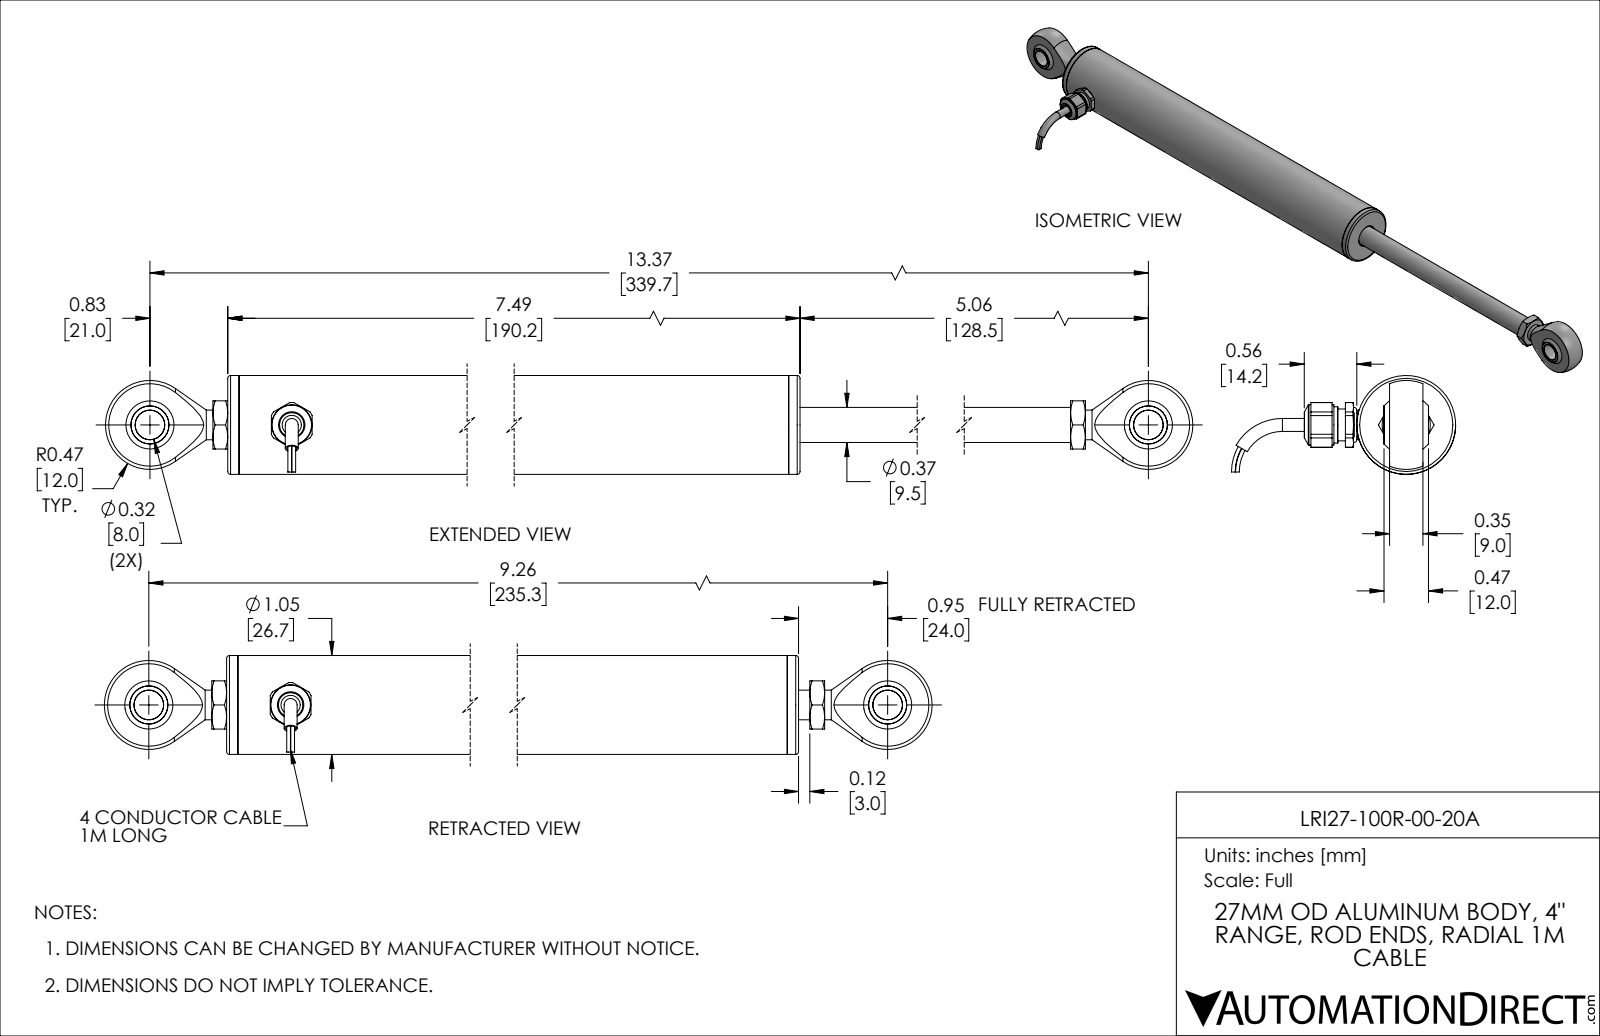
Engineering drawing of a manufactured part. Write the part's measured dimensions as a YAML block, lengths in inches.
part_name: "LRI27-100R-00-20A"
step_written_by: "SolidWorks 2019 (AUTOMOTIVE_DESIGN)"
units: inches
bodies: {solids: 25, faces: 279, planar: 108, cylindrical: 83, other: 88}
overall_size: [10.088, 2.382, 1.05]
volume: 4.474
surface_area: 92.13
round_holes:
  - {diameter: 0.268, count: 2}
  - {diameter: 0.106, count: 1}
  - {diameter: 0.138, count: 1}
  - {diameter: 0.156, count: 1}
  - {diameter: 0.187, count: 1}
  - {diameter: 0.201, count: 1}
  - {diameter: 0.205, count: 1}
  - {diameter: 0.25, count: 1}
  - {diameter: 0.274, count: 1}
  - {diameter: 0.313, count: 1}
  - {diameter: 0.36, count: 1}
  - {diameter: 0.375, count: 1}
round_bosses_or_shafts:
  - {diameter: 0.315, count: 4}
  - {diameter: 0.039, count: 4}
  - {diameter: 1.05, count: 1}
  - {diameter: 0.85, count: 1}
  - {diameter: 0.848, count: 1}
  - {diameter: 0.687, count: 1}
  - {diameter: 0.685, count: 1}
  - {diameter: 0.625, count: 1}
partial_cylinders:
  - {radius: 0.01, count: 2}
  - {radius: 0.067, count: 2}
  - {radius: 0.25, count: 2}
  - {radius: 0.197, count: 1}
  - {radius: 0.224, count: 1}
  - {radius: 0.238, count: 1}
face_to_face_distances: [0.12, 7.37, 0.354, 7.49, 0.862, 6.628, 5.161, 1.65, 0.788, 5.84]
